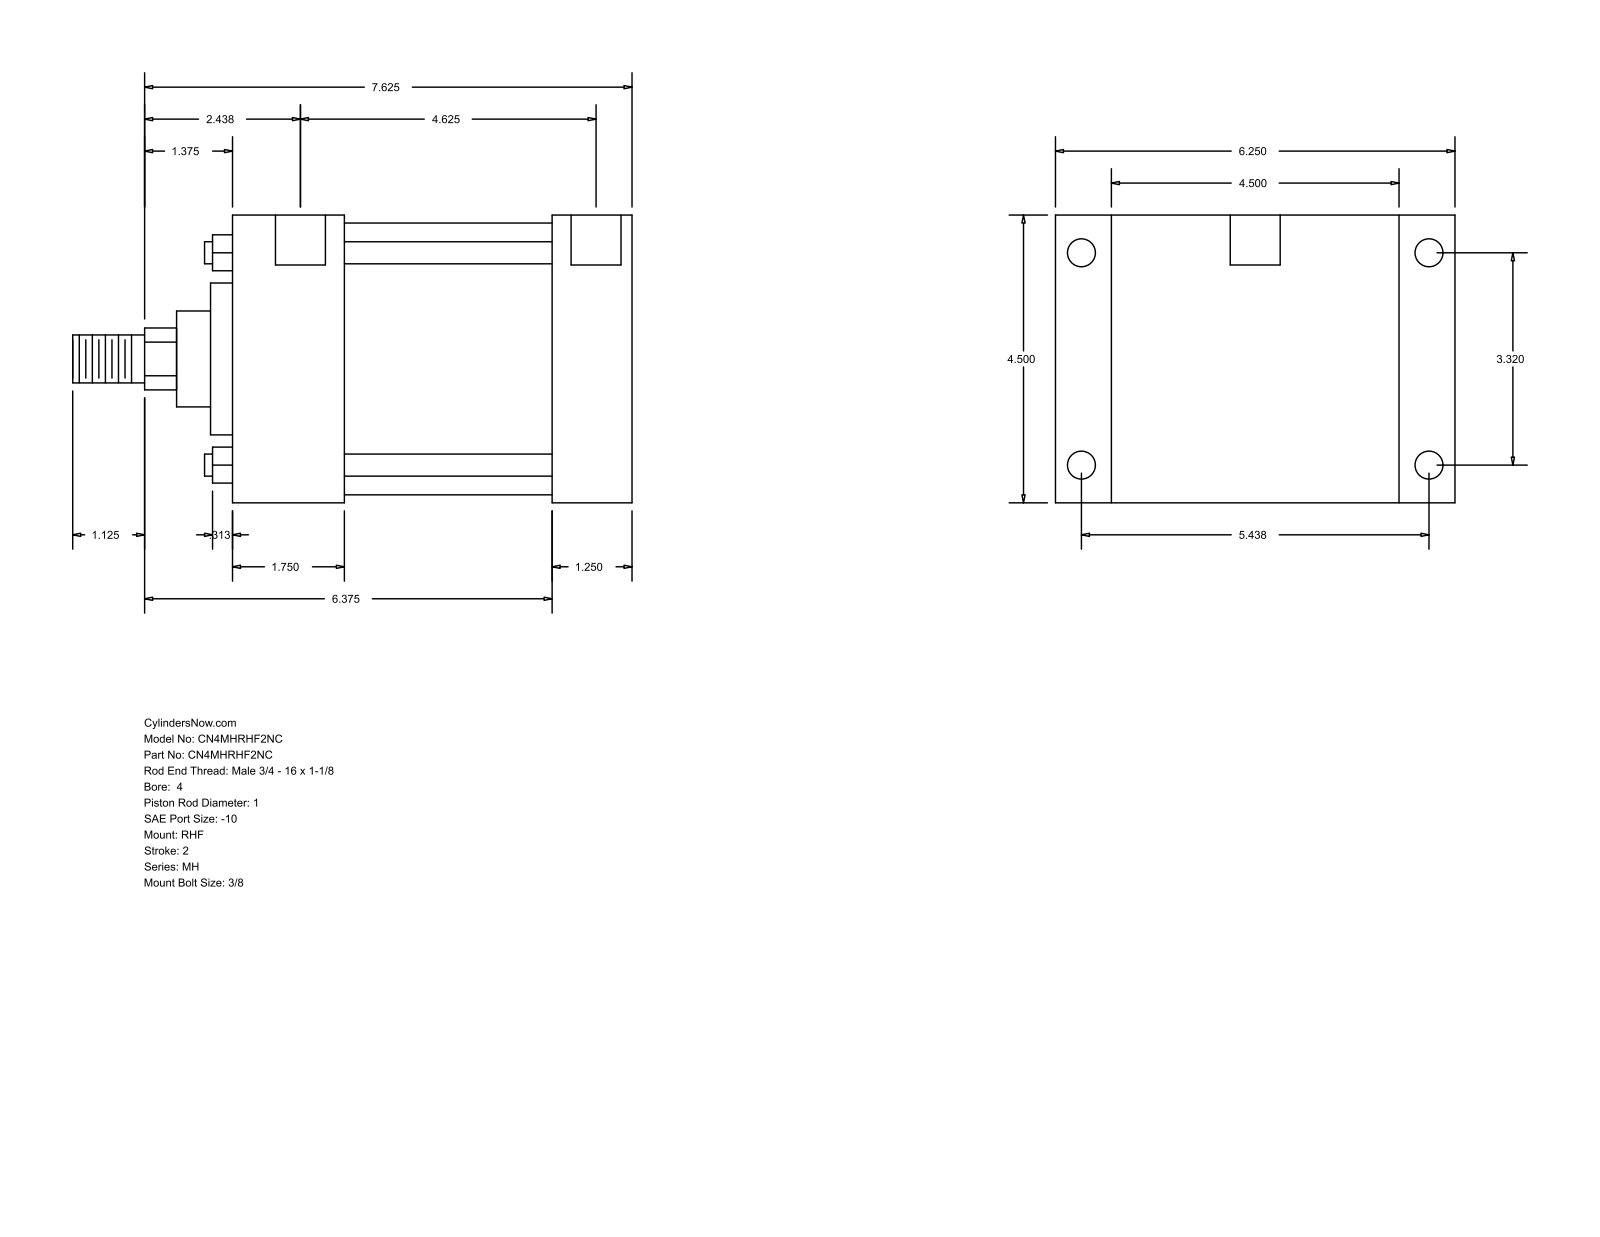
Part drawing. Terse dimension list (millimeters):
name: MH_RHF__0400_1
written by: GSSL Pune (CONFIG_CONTROL_DESIGN)
unit: mm
bodies: 0 solids, 90 faces (61 planar, 29 cylindrical, 0 other)
size: 222.25 × 158.75 × 114.3
holes: 4× ⌀8.73, 4× ⌀11.13, 2× ⌀19.84
bosses: 4× ⌀8.76, 1× ⌀107.95, 1× ⌀60.33, 1× ⌀38.1, 1× ⌀25.4, 1× ⌀19.05
rounds: 1× R12.29
face distances: 114.3, 158.76, 127.01, 31.75, 22.23, 136.53, 44.46, 82.55, 8.73, 53.19
hole spacings: 1.58, 84.32, 119.06, 120.64, 138.12, 161.82, 117.48
